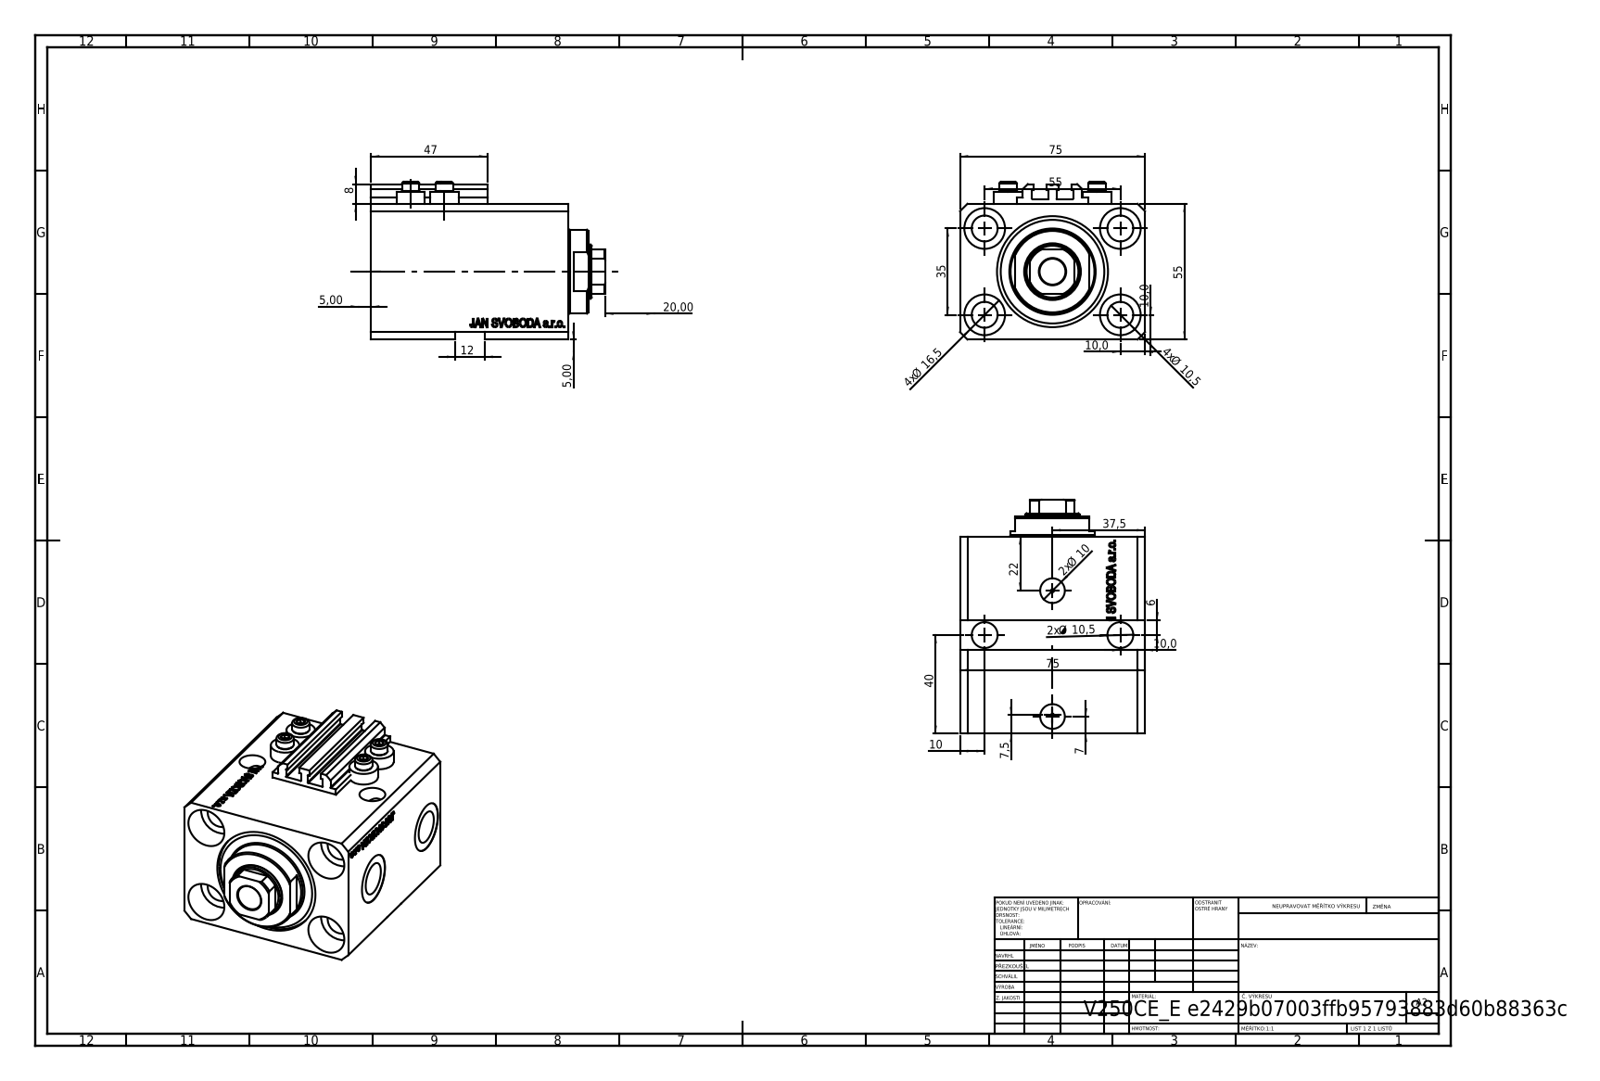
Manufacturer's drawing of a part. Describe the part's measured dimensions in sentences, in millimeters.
The part is named "ALLEN BOLT V250CE; V250CE_C_VCP; V250CE_VC_E; V250CE_E_Body". Its 3-D file was written by "SolidWorks 2019 (CONFIG_CONTROL_DESIGN)". It is 8 solids with 1064 faces: 514 planar, 126 cylindrical and 424 other. Overall it measures 94.9 by 75 by 64 millimeters. Its volume is 283 872 cubic millimeters and its surface area 77 066 square millimeters. Round holes: 7 of diameter 10.5, 4 of diameter 1.25, 4 of diameter 4, 4 of diameter 16.5, 2 of diameter 10, 2 of diameter 13.16, 2 of diameter 20, 1 of diameter 22, 1 of diameter 32, 1 of diameter 45. Round bosses or shafts: 4 of diameter 11.6, 4 of diameter 7, 1 of diameter 34. Partial cylindrical surfaces (rounded edges, fillets, slot ends): 10 of radius 0.2, 1 of radius 10.5. The main face-to-face distances are 55, 75, 80, 52.9, 27.1, 3, 9.9, 43, 70.1, 23. The hole center spacings are 32.6, 55, 13.6, 14.09, 19.89, 20.12, 25.81, 28.48.
